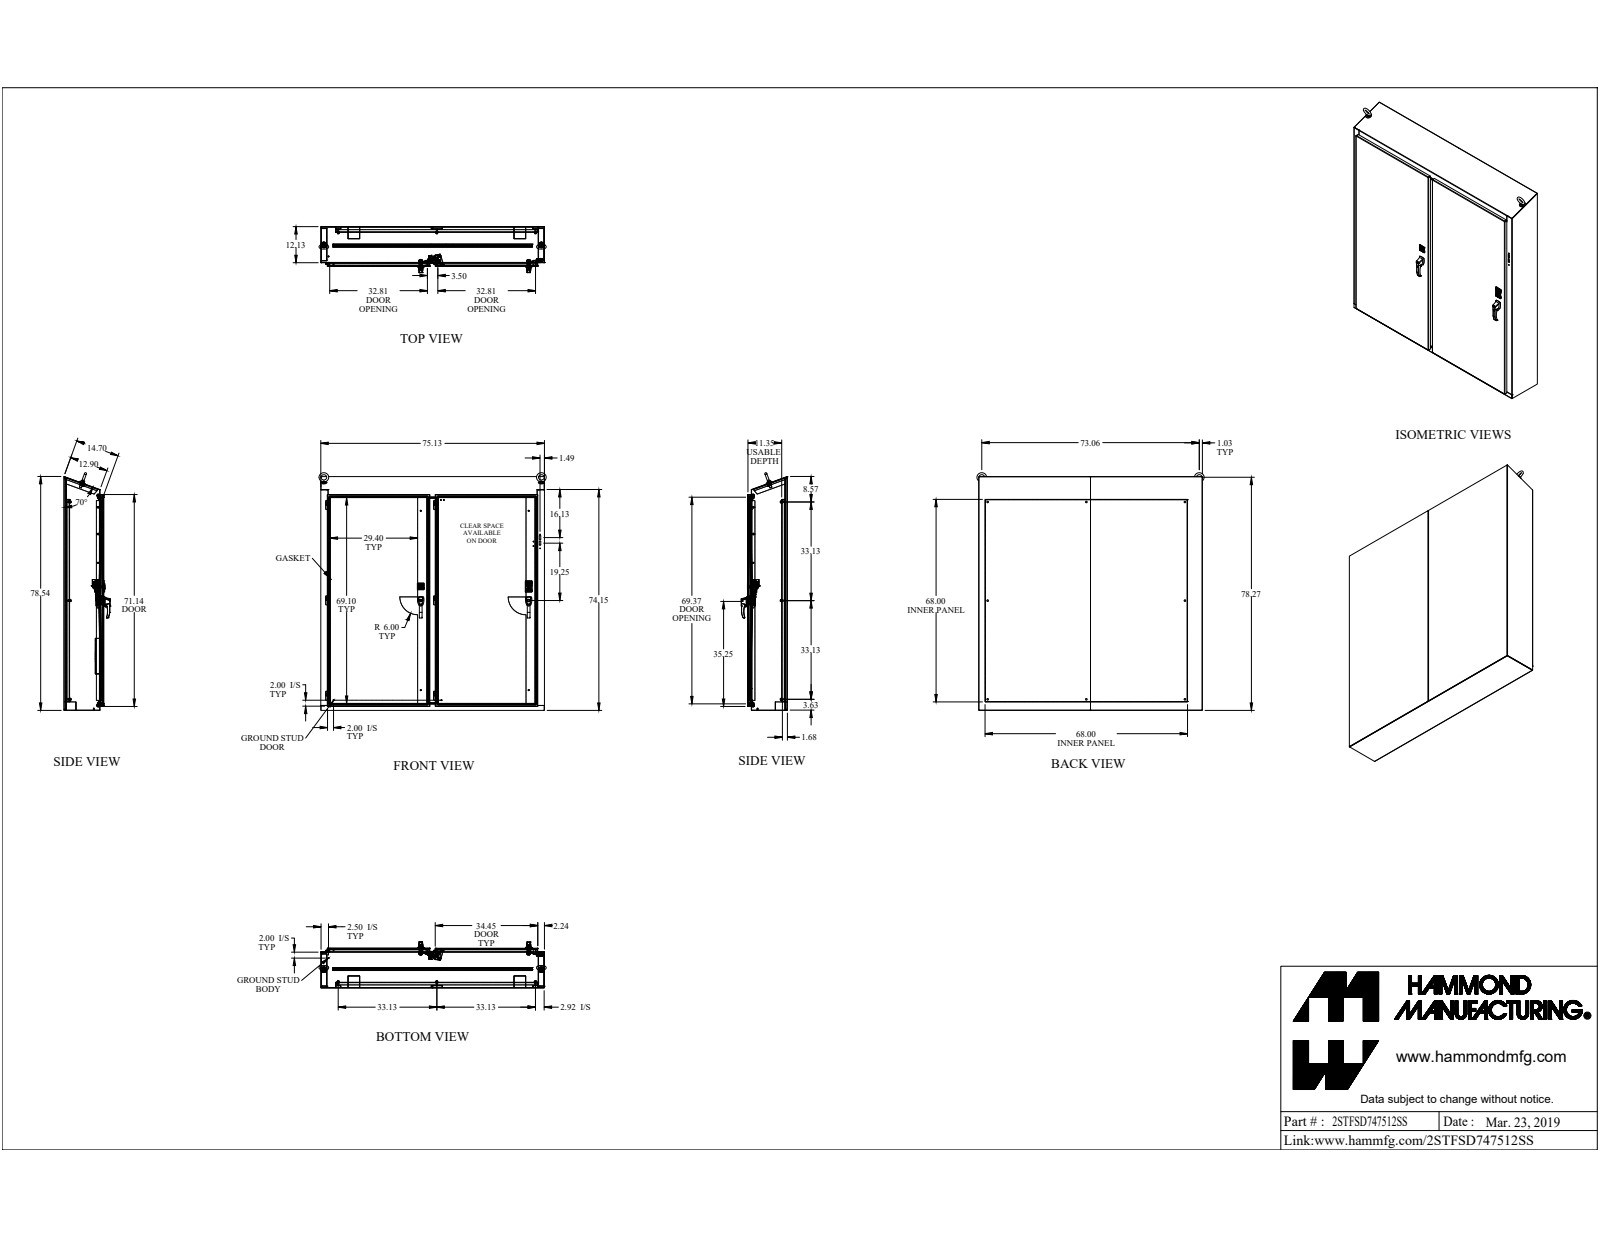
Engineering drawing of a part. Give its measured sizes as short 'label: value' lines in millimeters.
name: 2STFSD747512SS
written by: SolidWorks 2019 (CONFIG_CONTROL_DESIGN)
unit: mm
bodies: 210 solids, 3274 faces (1902 planar, 992 cylindrical, 380 other)
size: 2026.7 × 1938.2 × 393.5
volume: 39 940 000 mm³; area: 31 170 000 mm²
holes: 11× ⌀5, 9× ⌀6.4, 9× ⌀7.1, 9× ⌀7.8, 8× ⌀8.9, 8× ⌀14.3, 6× ⌀6.5, 6× ⌀8, 6× ⌀11.3, 4× ⌀7.1, 4× ⌀7.2, 4× ⌀9.5
bosses: 18× ⌀6.4, 14× ⌀25.4, 9× ⌀16.5, 9× ⌀9.5, 8× ⌀8.4, 6× ⌀19.1, 5× ⌀15.9, 5× ⌀12.7
rounds: 64× R3.2, 36× R1.2, 36× R3.6, 34× R12.7, 28× R0.8, 27× R1.5, 24× R6.4, 20× R0.3
face distances: 2.4, 2.4, 336.7, 3.2, 46, 48.4, 42.8, 45.3, 0.6, 288.9
hole spacings: 1855.7, 1881.4, 1682.8, 750.4, 841.4, 841.4, 915.3, 1042
